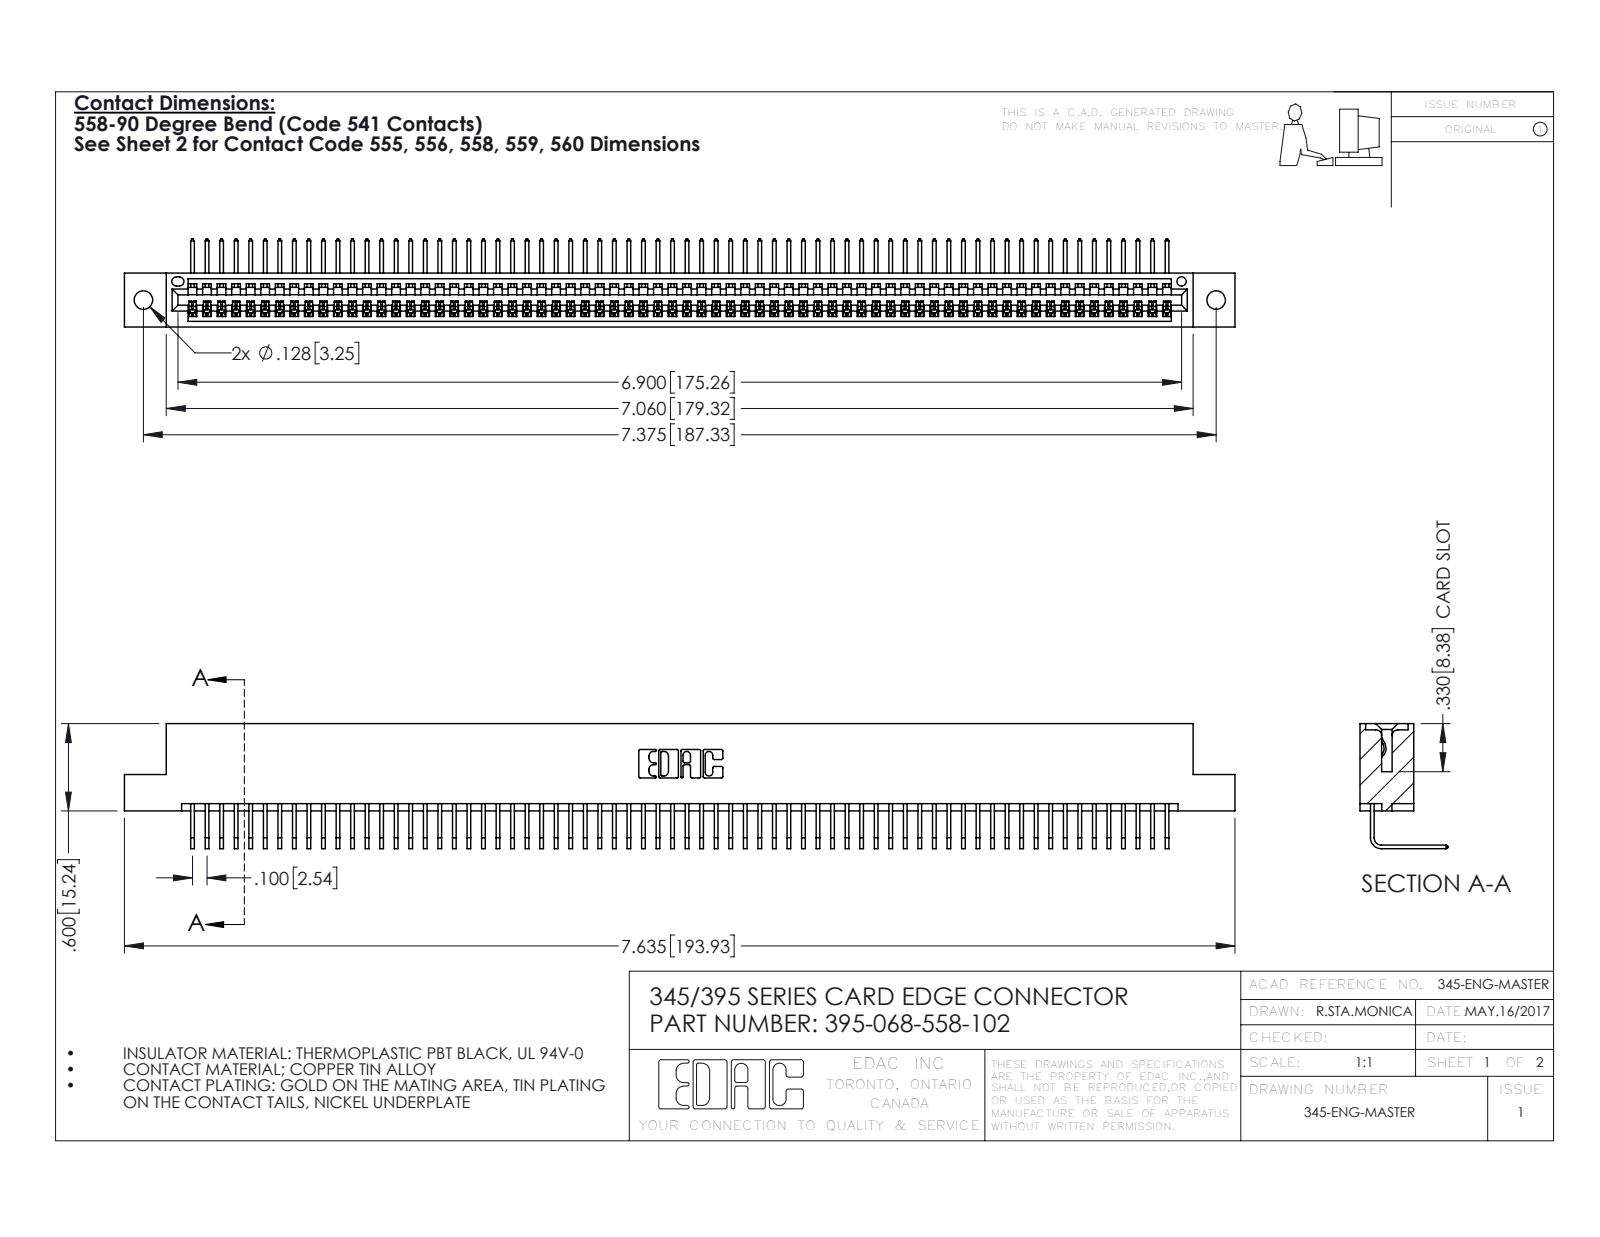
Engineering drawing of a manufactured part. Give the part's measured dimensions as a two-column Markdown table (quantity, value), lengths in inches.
| quantity | value |
| --- | --- |
| part name | 345-292-001_558 Tail - 2; 395-068-558-102; 345 Part_Flush Mounting Lugs - 0.128 Dia |
| STEP written by | SolidWorks 2016 (CONFIG_CONTROL_DESIGN) |
| units | inches |
| bodies | 69 solids, 4206 faces (2936 planar, 1270 cylindrical, 0 other) |
| overall size | 7.635 × 0.859 × 0.605 |
| volume | 1.149 in³ |
| surface area | 40.96 in² |
| round holes (diameter × count) | 0.128 × 2, 0.064 × 1 |
| partial cylindrical surfaces (radius × count) | 0.006 × 136, 0.01 × 22, 0.007 × 6, 0.031 × 6, 0.026 × 3, 0.031 × 2, 0.04 × 2, 0.014 × 1 |
| main face-to-face distances | 0.298, 0.072, 0.37, 0.2, 0.098, 0.272, 0.025, 0.225, 0.149, 0.072 |
| hole center spacings | 0.27, 7.139, 7.375 |
